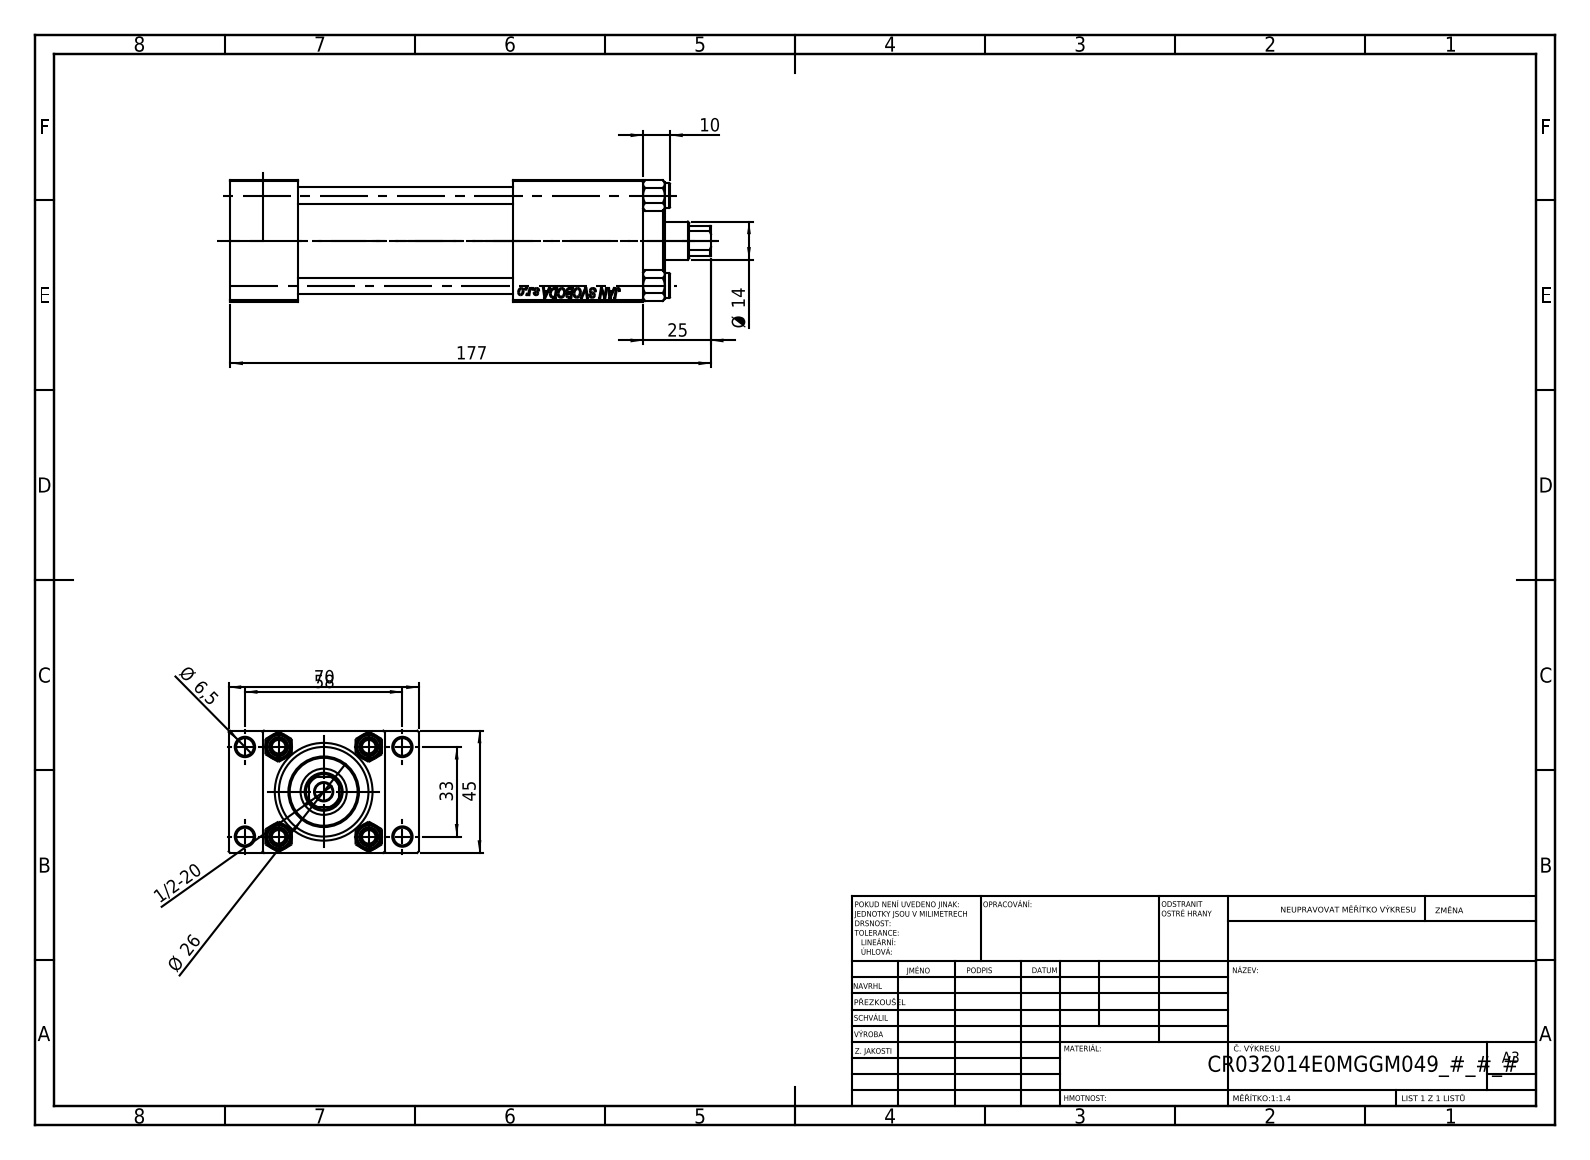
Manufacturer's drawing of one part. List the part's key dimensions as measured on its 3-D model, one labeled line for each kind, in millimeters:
Part name (STEP PRODUCT): V215CR_TYCINKA_E; NUT_M5_E; V215CR_VCP_E; V215CR_E_Body (+1 more)
STEP written by: SolidWorks 2019 (CONFIG_CONTROL_DESIGN)
Units: millimetres
Bodies: 11 solids, 1136 faces (497 planar, 87 cylindrical, 552 other)
Overall size (bounding box): 177 × 70 × 45
Volume: 237 383 mm³ · Surface area: 85 912 mm²
Round holes (diameter × count): ⌀6.5 ×5, ⌀6 ×4, ⌀7 ×2, ⌀13.16 ×2, ⌀20 ×2, ⌀14 ×1, ⌀17 ×1, ⌀24 ×1, ⌀32 ×1, ⌀33 ×1
Round bosses / shafts (diameter × count): ⌀9 ×4, ⌀38 ×1, ⌀26 ×1
Partial cylindrical surfaces — rounded edges, fillets, slot ends (radius × count): R6.5 ×1
Main face-to-face distances: 45, 25, 12.5, 57.5, 152, 127, 70, 104, 79, 48
Hole centre spacings: 12.4, 23.48, 33.2, 33.37, 35.35, 45.6, 56.35, 33
